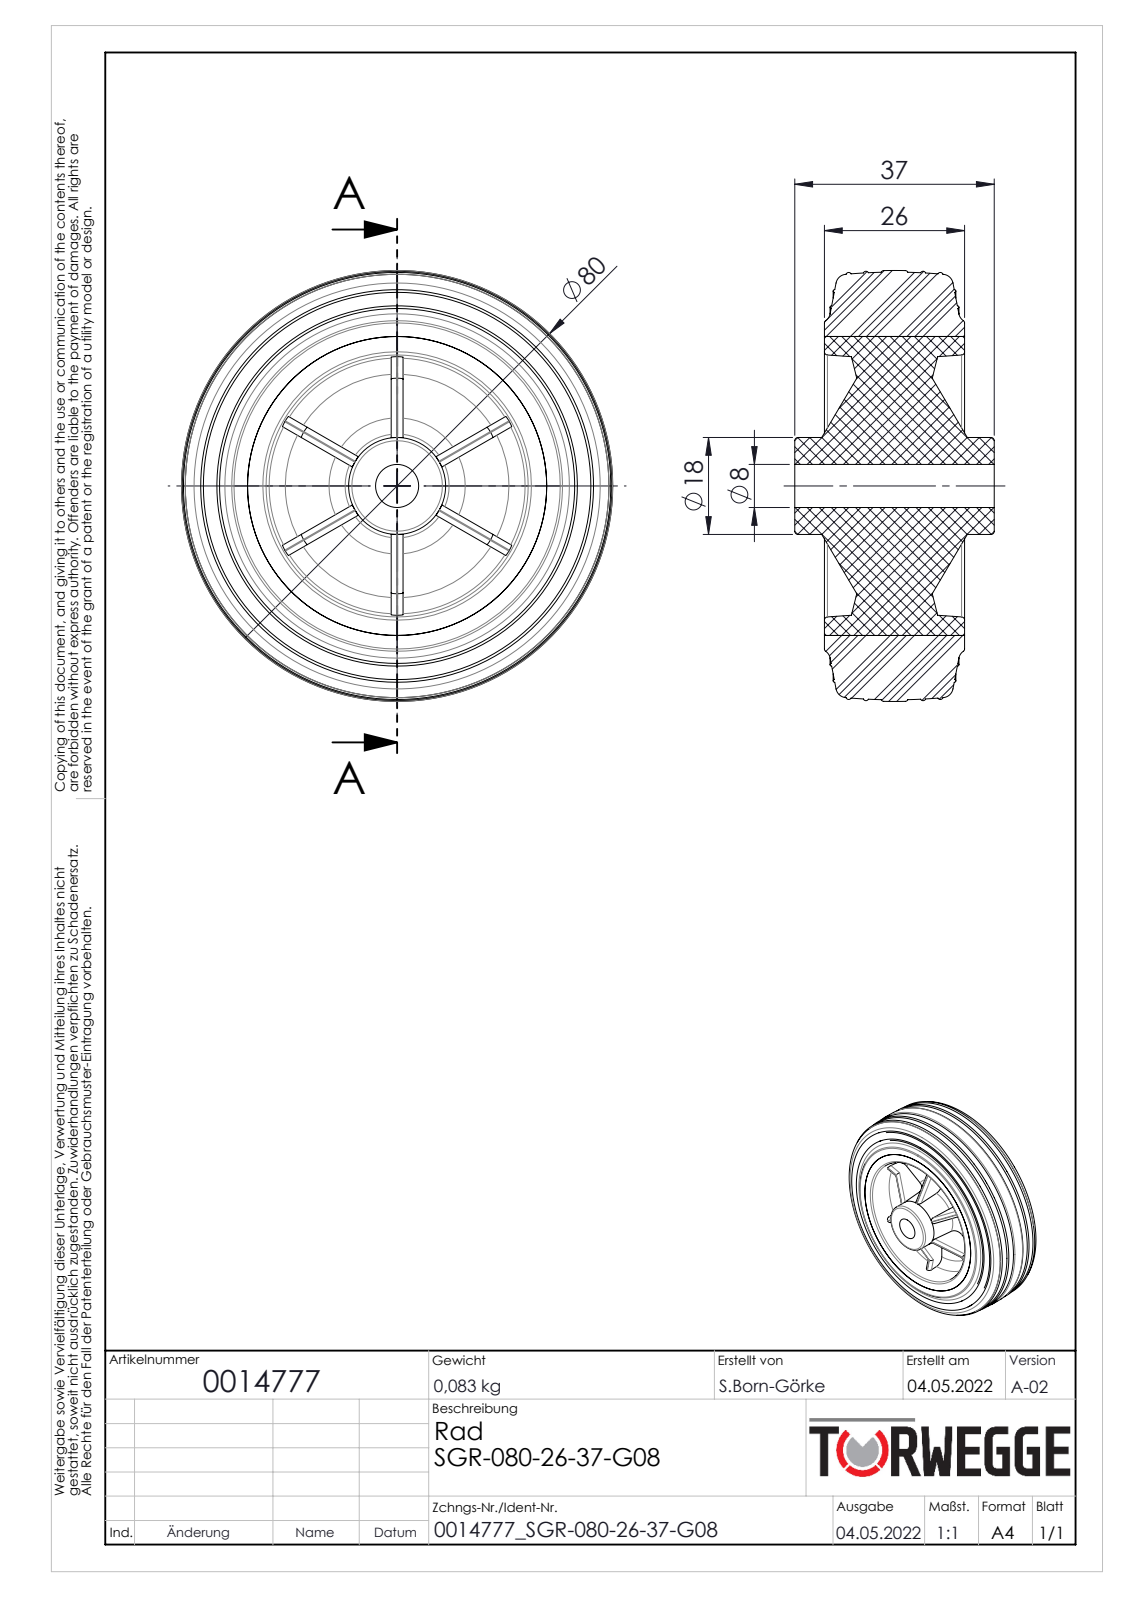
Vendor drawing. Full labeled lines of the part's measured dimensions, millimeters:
Part name (STEP PRODUCT): 0014777
STEP written by: SolidWorks 2020 (AUTOMOTIVE_DESIGN)
Units: millimetres
Bodies: 2 solids, 256 faces (66 planar, 62 cylindrical, 128 other)
Overall size (bounding box): 80 × 80 × 37
Volume: 90 911 mm³ · Surface area: 32 065 mm²
Round holes (diameter × count): ⌀8 ×1, ⌀55.5 ×1
Round bosses / shafts (diameter × count): ⌀18 ×1
Partial cylindrical surfaces — rounded edges, fillets, slot ends (radius × count): R1 ×48
Main face-to-face distances: 11.5, 14.5, 2.2, 26, 3, 5.5, 17, 20, 31.5, 37
